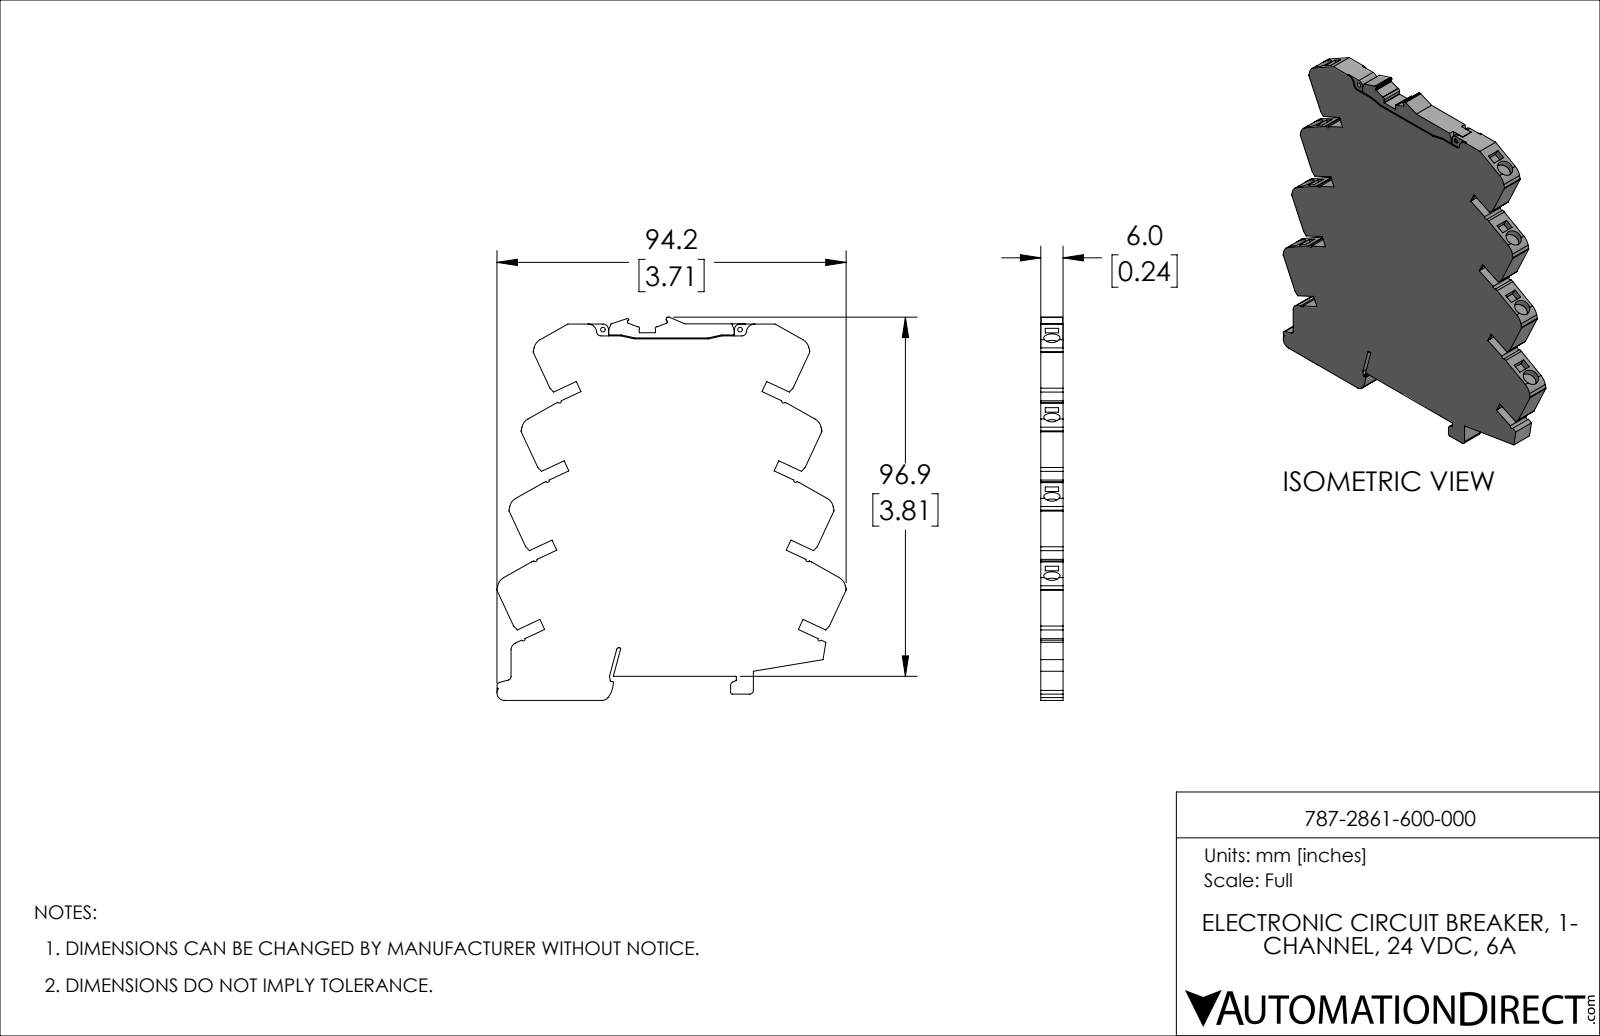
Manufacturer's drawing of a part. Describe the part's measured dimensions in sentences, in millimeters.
The part is named "787-2861/600-000". Its 3-D file was written by "PARTsolutions (CONFIG_CONTROL_DESIGN)". It is 1 solid with 294 faces: 219 planar, 75 cylindrical and 0 other. Overall it measures 103.36 by 94.26 by 6 millimeters. Its volume is 43 932 cubic millimeters and its surface area 19 262 square millimeters. Round holes: 8 of diameter 4.4, 2 of diameter 1.25. Partial cylindrical surfaces (rounded edges, fillets, slot ends): 12 of radius 0.5, 11 of radius 0.2, 8 of radius 0.4, 8 of radius 3.35, 4 of radius 1, 3 of radius 0.3, 3 of radius 2, 2 of radius 0.45. The main face-to-face distances are 6, 17.99, 17.02, 12.01, 5.9, 12, 3, 24.01, 35.98, 6.5. The hole center spacings are 13.35, 13.34, 26.7, 26.69, 26.71, 37, 40.04, 40.05.
